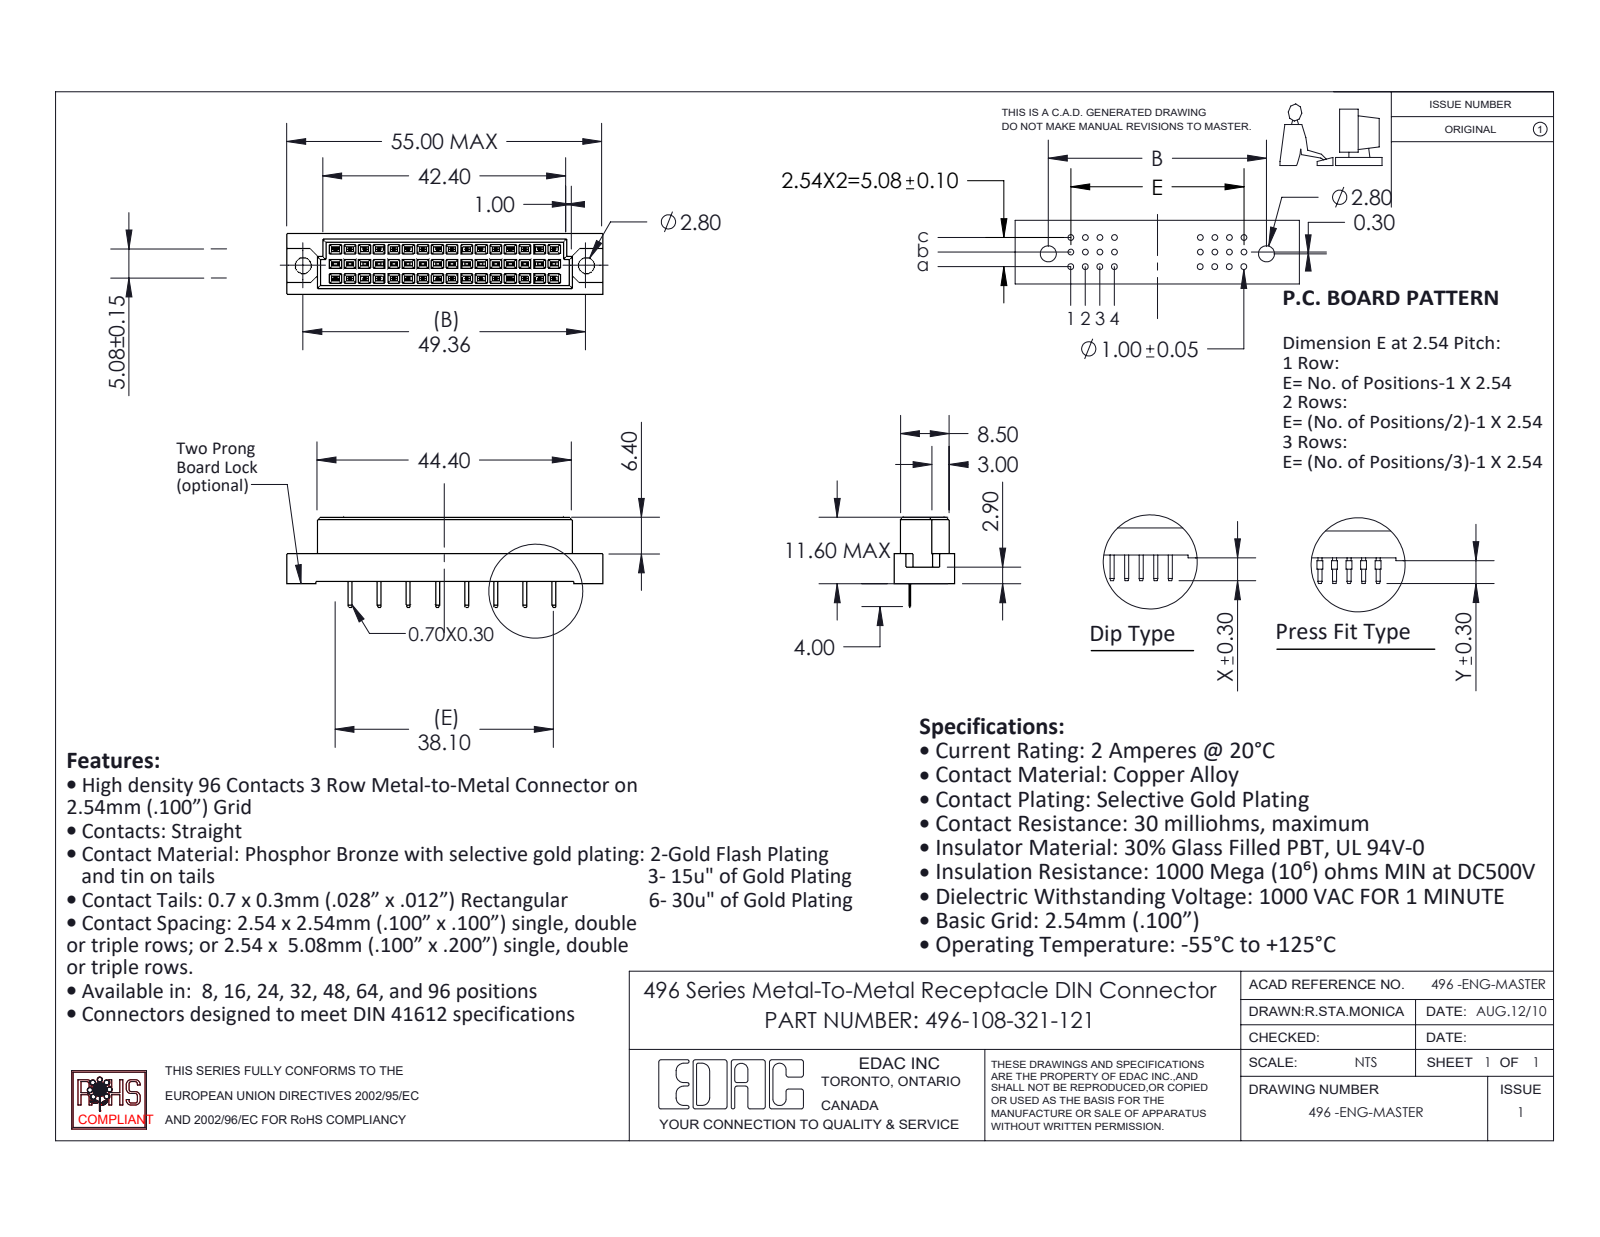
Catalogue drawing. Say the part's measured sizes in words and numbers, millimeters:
The part is named "496-290_21; 496 Part_48; 496-108-321-121". Its 3-D file was written by "SolidWorks 2020 (CONFIG_CONTROL_DESIGN)". It is 9 solids with 746 faces: 742 planar, 4 cylindrical and 0 other. Overall it measures 55 by 15.6 by 10.6 millimeters. Its volume is 4 604 cubic millimeters and its surface area 4 357 square millimeters. Round holes: 2 of diameter 2.8. The main face-to-face distances are 2.54, 5.08, 1.05, 9.55, 0.81, 10.6, 3.35, 1.73, 8.5, 0.56. The hole center spacings are 49.36.
